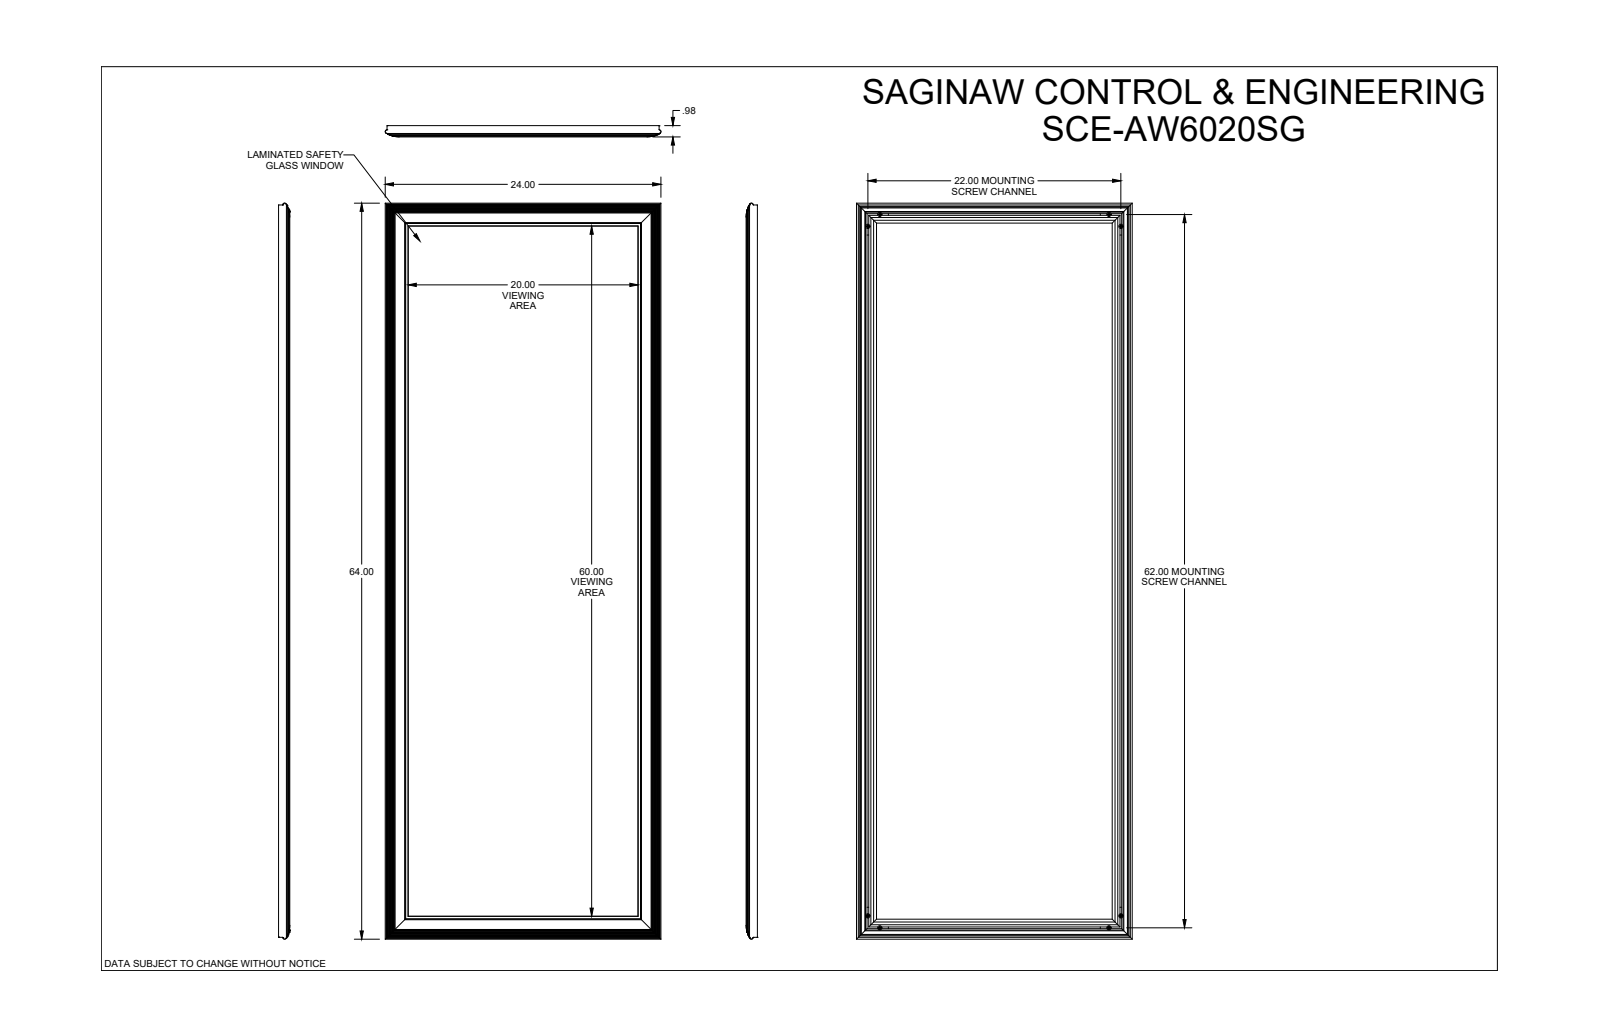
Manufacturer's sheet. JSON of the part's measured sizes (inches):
{"part_name": "SCE-AW6020SG", "step_written_by": "SolidWorks 2019 (CONFIG_CONTROL_DESIGN)", "units": "inches", "bodies": {"solids": 25, "faces": 1202, "planar": 454, "cylindrical": 308, "other": 440}, "overall_size": [63.976, 23.976, 0.98], "volume_in3": 397.3, "surface_area_in2": 5009, "round_holes": [[0.148, 8], [0.165, 4]], "round_bosses_or_shafts": [[0.19, 8], [0.122, 8]], "partial_cylinders_radius": [[0.02, 156], [0.059, 24], [0.01, 16], [0.03, 12], [0.016, 4], [0.02, 4], [0.06, 4], [0.157, 4]], "face_to_face_distances": [0.236, 0.06, 0.065, 0.075, 0.216, 0.02, 1.52, 0.563, 0.2, 0.313], "hole_center_spacings": [1.474, 20.999, 60.983, 64.48, 19.931, 22.016, 59.931, 62.016]}
